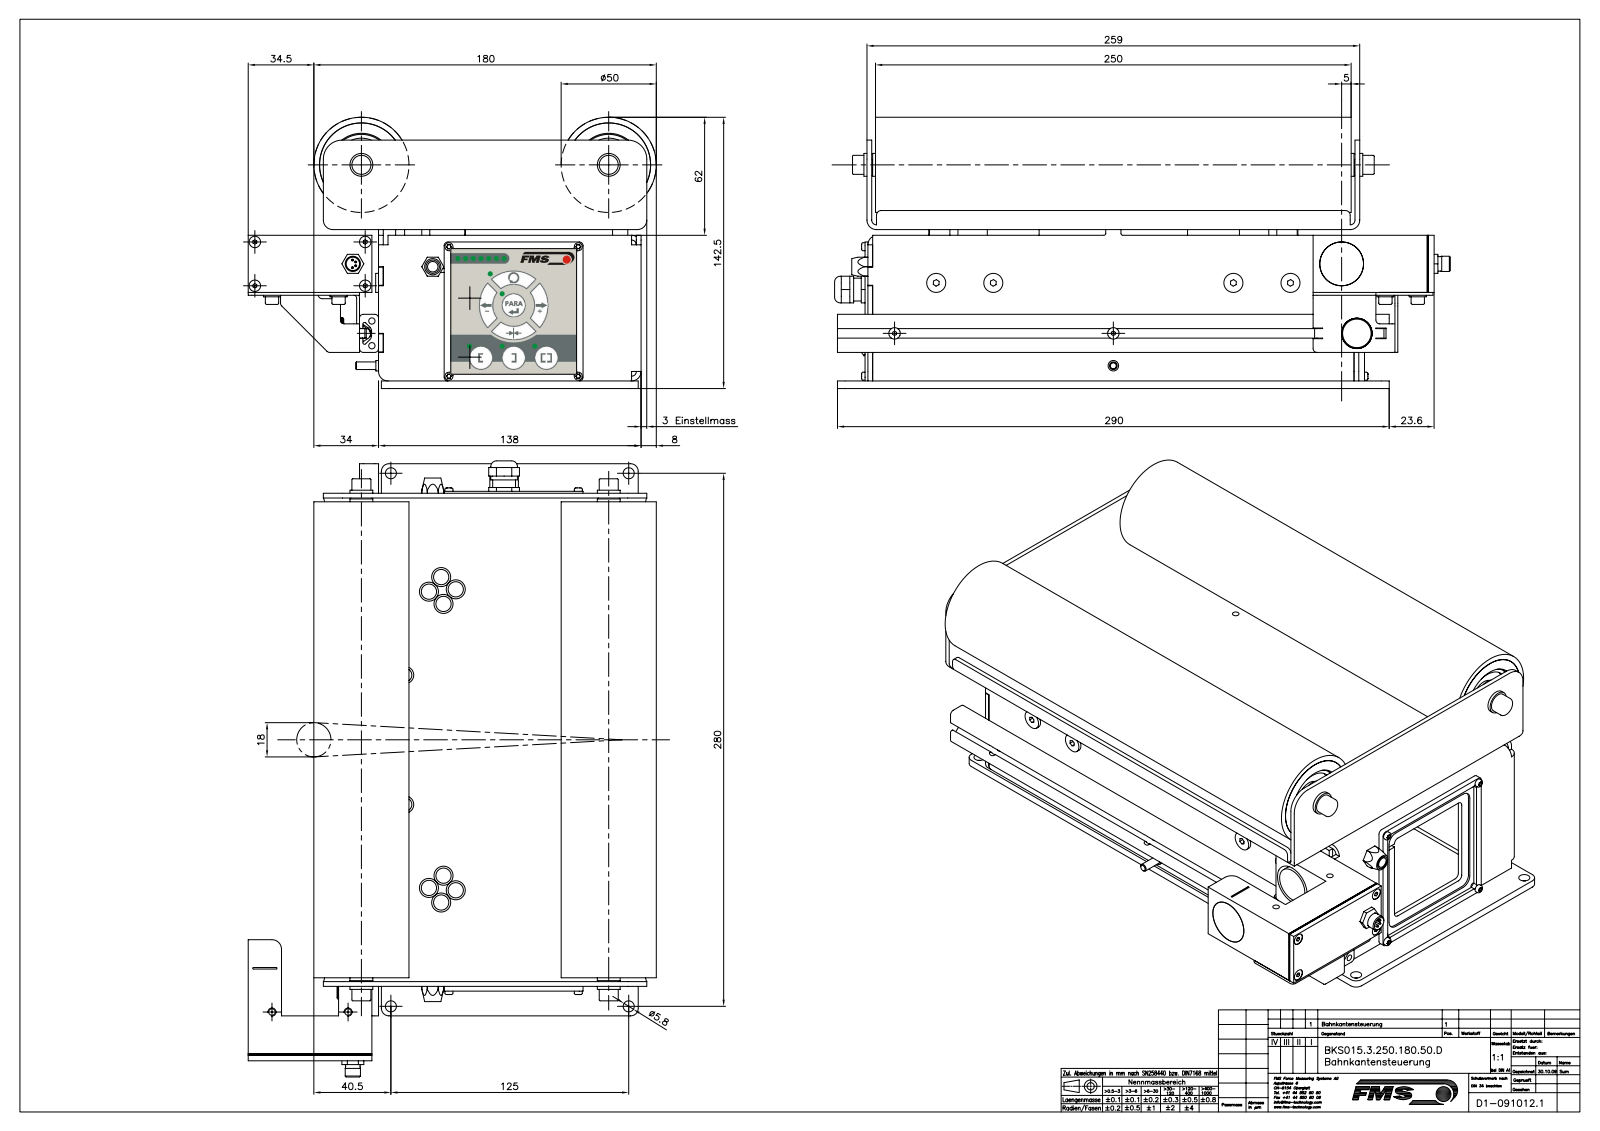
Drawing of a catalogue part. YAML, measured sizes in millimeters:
part_name: "K0910121_STP; K0910125; K0910124; K0901207 (+8 more)"
step_written_by: "Mechanical Desktop 2009 (CONFIG_CONTROL_DESIGN)"
units: millimeters
bodies: {solids: 110, faces: 2730, planar: 1293, cylindrical: 1109, other: 328}
overall_size: [323.6, 214.5, 142.5]
volume: 1027000
surface_area: 681205
round_holes:
  - {diameter: 3.2, count: 18}
  - {diameter: 4.5, count: 15}
  - {diameter: 6, count: 10}
  - {diameter: 2.5, count: 8}
  - {diameter: 2.14, count: 7}
  - {diameter: 2.6, count: 7}
  - {diameter: 4.3, count: 7}
  - {diameter: 5.4, count: 7}
  - {diameter: 4.2, count: 5}
  - {diameter: 1.9, count: 4}
  - {diameter: 3.42, count: 4}
  - {diameter: 5.3, count: 4}
round_bosses_or_shafts:
  - {diameter: 4, count: 21}
  - {diameter: 8, count: 17}
  - {diameter: 10, count: 10}
  - {diameter: 7, count: 8}
  - {diameter: 12, count: 7}
  - {diameter: 9, count: 7}
  - {diameter: 7.9, count: 7}
  - {diameter: 3, count: 7}
partial_cylinders:
  - {radius: 0.25, count: 48}
  - {radius: 2.5, count: 37}
  - {radius: 2, count: 25}
  - {radius: 5, count: 21}
  - {radius: 1, count: 8}
  - {radius: 3.15, count: 8}
  - {radius: 3, count: 7}
  - {radius: 4, count: 5}
face_to_face_distances: [2.5, 4, 79.5, 86, 82, 83.5, 3, 0.5, 135.5, 2]
hole_center_spacings: [66.18, 68, 116, 2.62, 11.77, 30.34, 56.68, 64.3]
